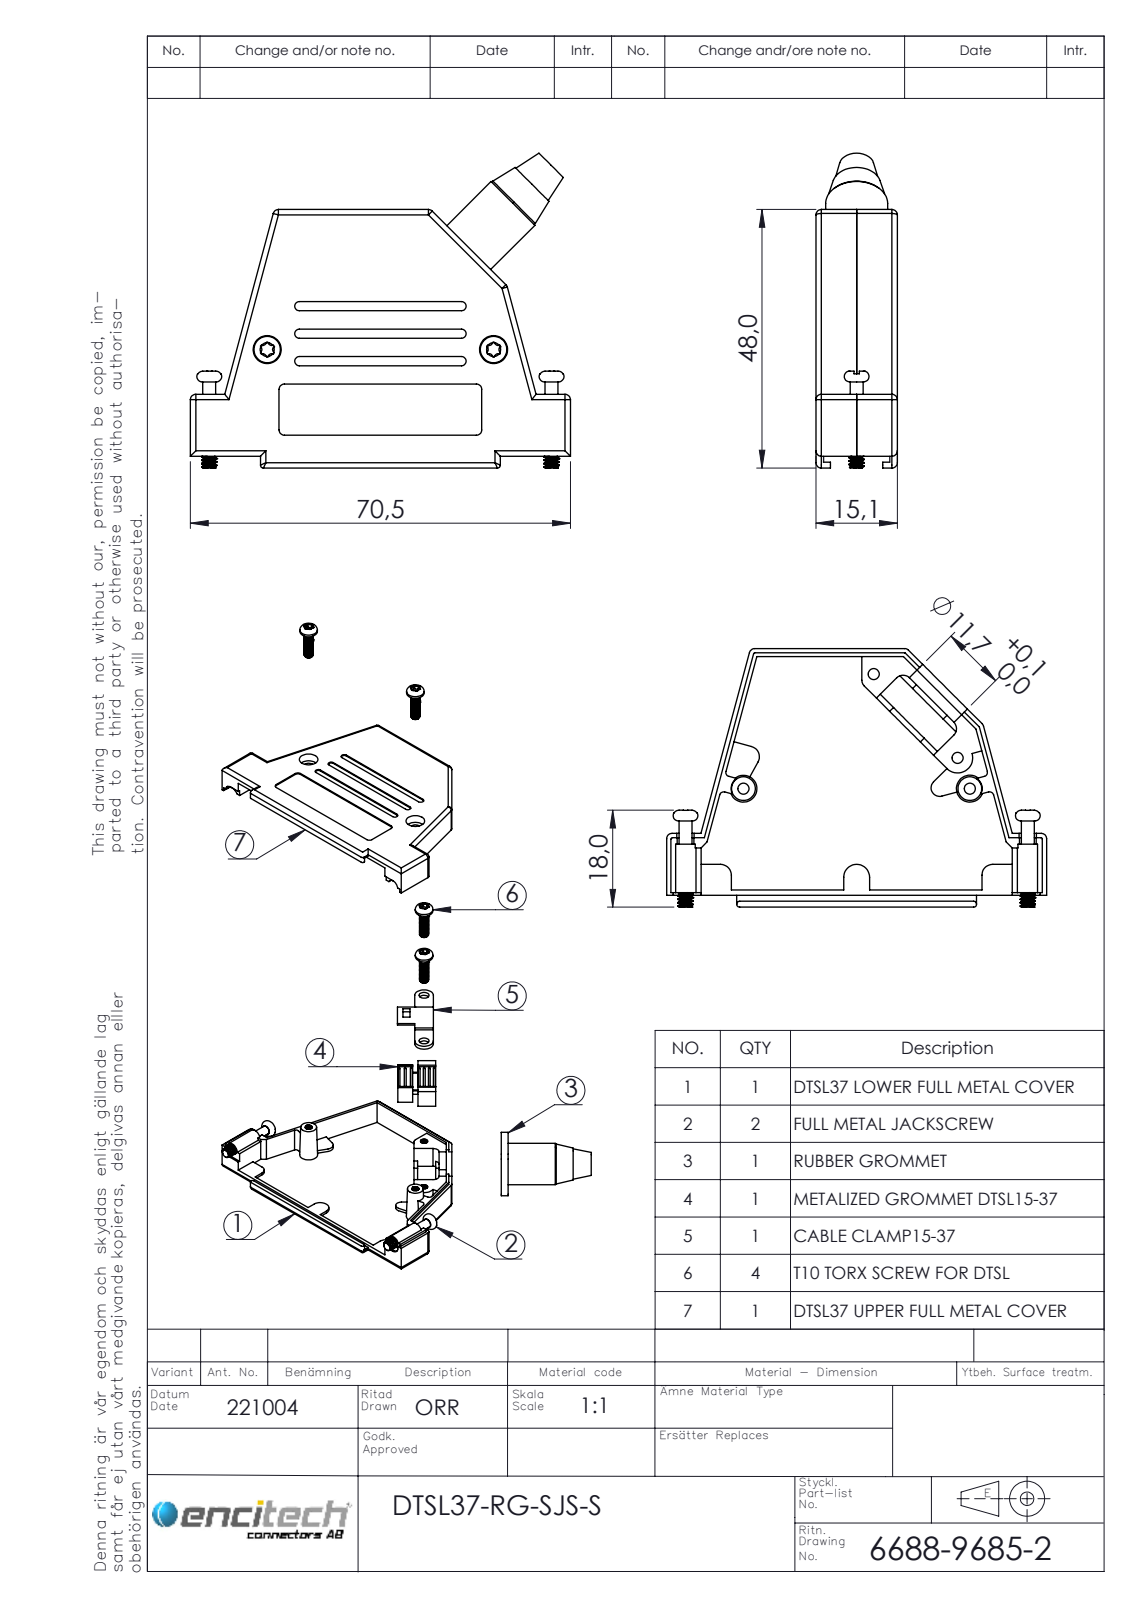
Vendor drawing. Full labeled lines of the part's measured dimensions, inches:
Part name (STEP PRODUCT): 6844-0104-01; 6688-9685-2; 6830-0108-04; 6805-0208-04 (+4 more)
STEP written by: SolidWorks 2021 (AUTOMOTIVE_DESIGN)
Units: inches
Bodies: 15 solids, 1066 faces (387 planar, 571 cylindrical, 108 other)
Overall size (bounding box): 2.776 × 2.302 × 0.594
Volume: 0.827 in³ · Surface area: 30.23 in²
Round holes (diameter × count): ⌀0.081 ×4, ⌀0.11 ×4, ⌀0.122 ×2, ⌀0.126 ×2, ⌀0.205 ×2, ⌀0.354 ×1, ⌀0.461 ×1
Round bosses / shafts (diameter × count): ⌀0.193 ×4, ⌀0.098 ×4, ⌀0.276 ×2, ⌀0.11 ×2, ⌀0.094 ×2, ⌀0.453 ×1, ⌀0.437 ×1
Partial cylindrical surfaces — rounded edges, fillets, slot ends (radius × count): R0.039 ×37, R0.007 ×24, R0.028 ×24, R0.033 ×12, R0.079 ×12, R0.012 ×4, R0.03 ×4, R0.008 ×2
Main face-to-face distances: 0.059, 0.535, 0.476, 0.594, 0.047, 0.583, 0.524, 0.238, 0.297, 0.285
Hole centre spacings: 0.242, 0.866, 1.093, 1.267, 1.58, 1.654, 2.5
